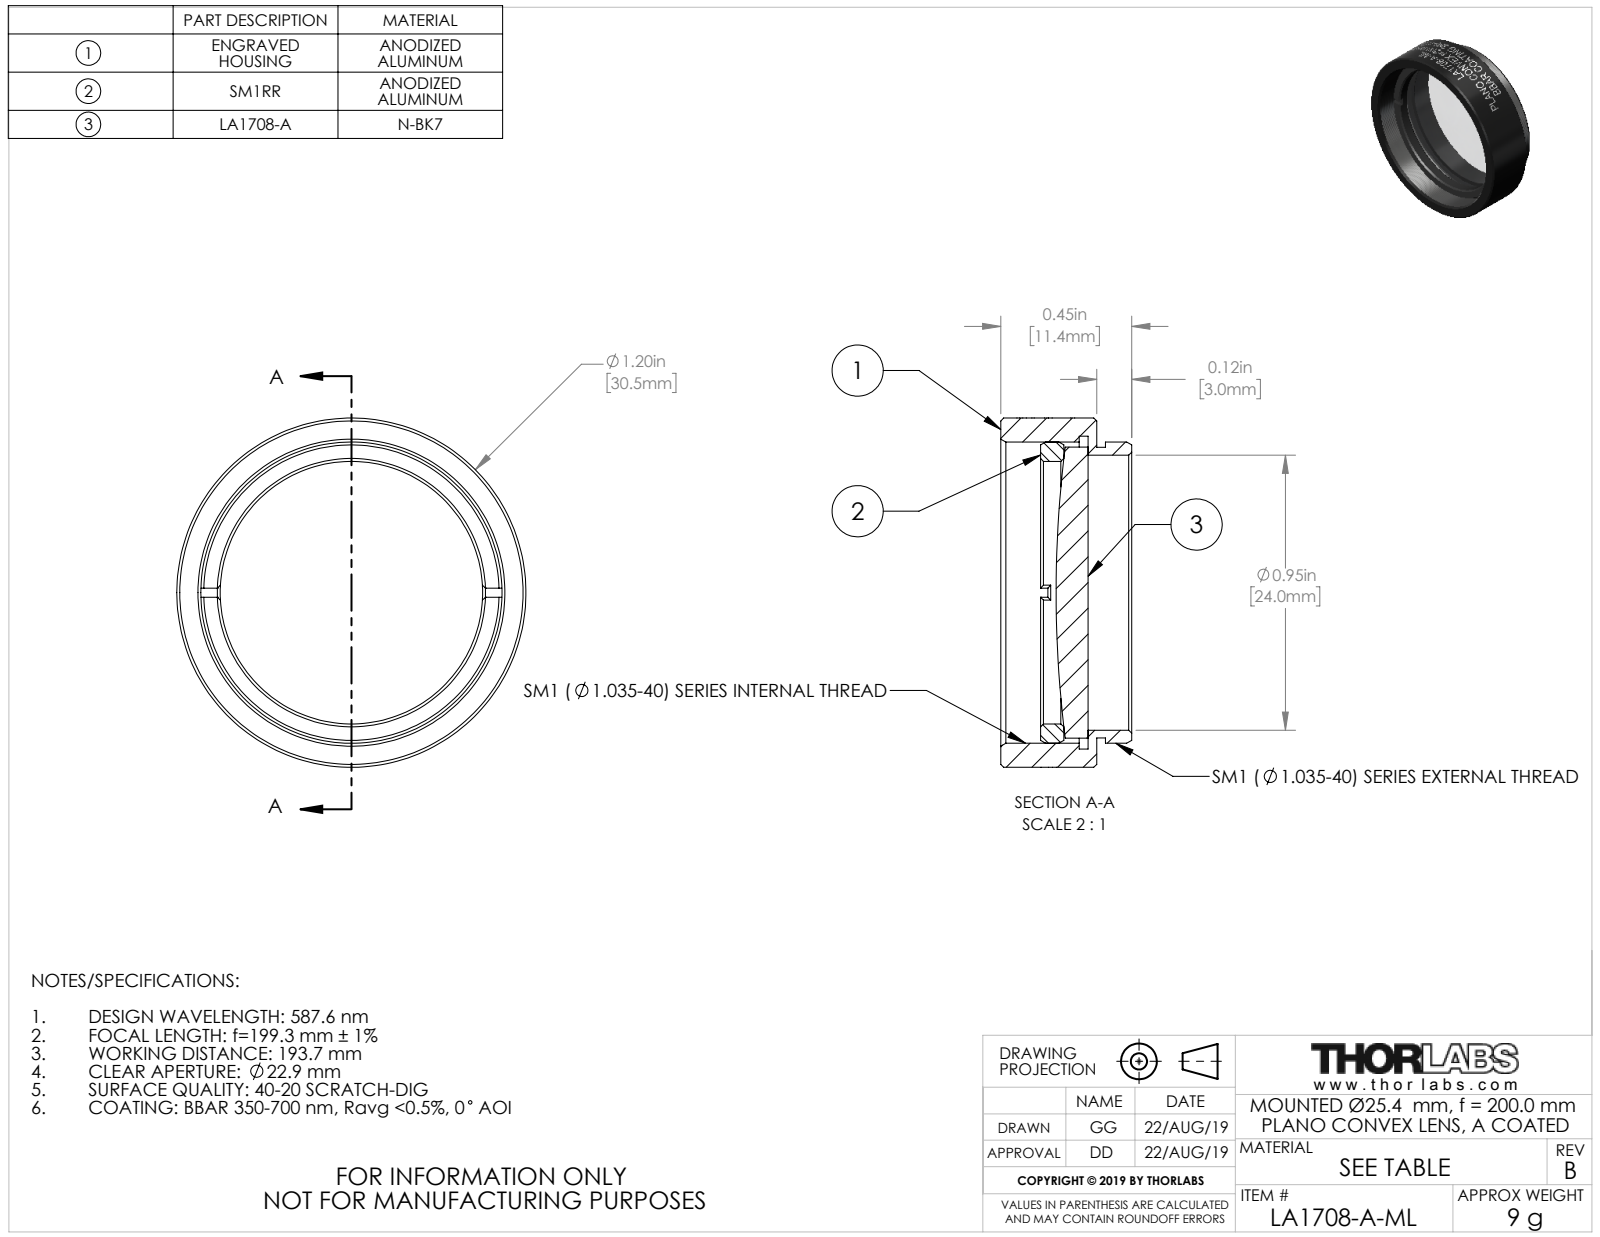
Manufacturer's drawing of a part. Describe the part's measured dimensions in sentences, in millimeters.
The part is named "24439-E0W". Its 3-D file was written by "SolidWorks 2018 (CONFIG_CONTROL_DESIGN)". It is 3 solids with 154 faces: 20 planar, 110 cylindrical and 24 other. Overall it measures 30.48 by 30.48 by 11.43 millimeters. Its volume is 3 291 cubic millimeters and its surface area 4 314 square millimeters. Round holes: 1 of diameter 22.91, 1 of diameter 24, 1 of diameter 27.3. Round bosses or shafts: 1 of diameter 30.48, 1 of diameter 26.29, 1 of diameter 25.4, 1 of diameter 25.37. The main face-to-face distances are 0.76, 8.38, 7.62, 2.87, 2.11, 5.51, 4.9, 4.14, 2.03, 3.48.
